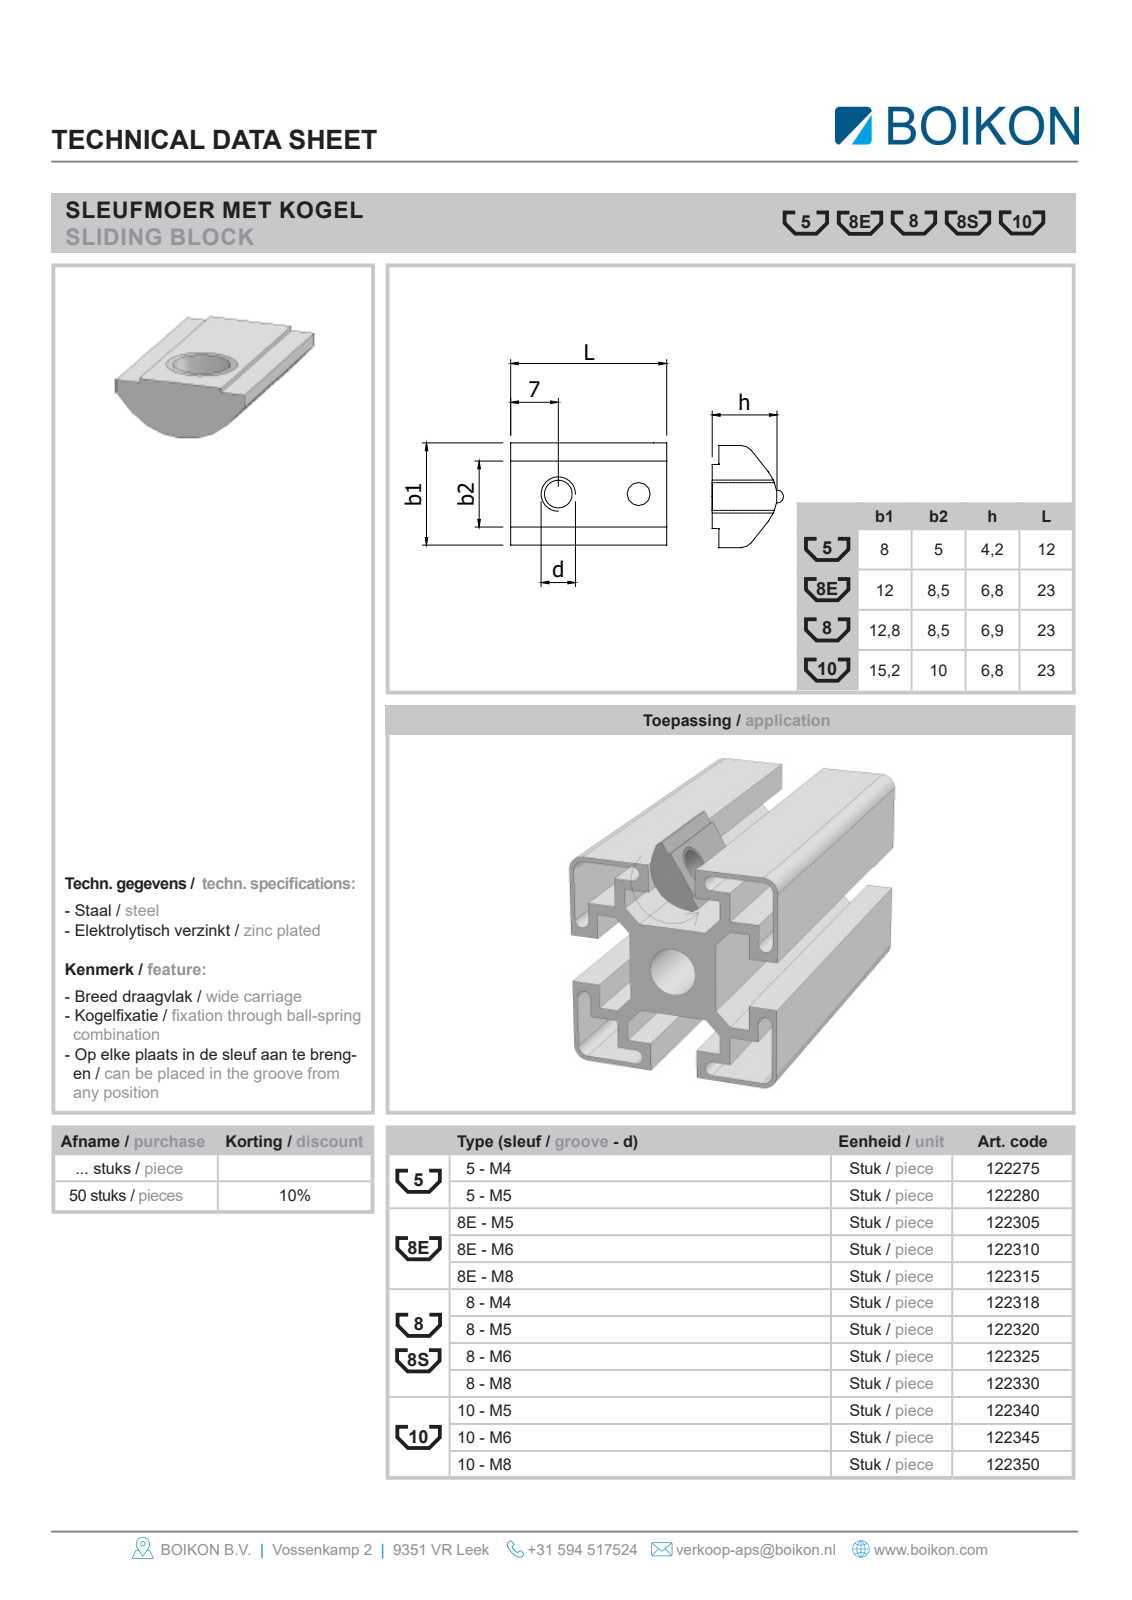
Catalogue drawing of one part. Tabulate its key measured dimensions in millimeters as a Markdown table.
| quantity | value |
| --- | --- |
| part name | Root; 122345Sleufmoer 10 - M6 met kogelBOIKON |
| STEP written by | HiCAD 2013 1802.4 Build 509 (AUTOMOTIVE_DESIGN) |
| units | millimeters |
| bodies | 1 solid, 14 faces (11 planar, 2 cylindrical, 1 other) |
| overall size | 23 × 15.3 × 13.1 |
| volume | 1 597 mm³ |
| surface area | 1 095 mm² |
| round holes (diameter × count) | 6 × 1 |
| partial cylindrical surfaces (radius × count) | 8 × 1 |
| main face-to-face distances | 0.5, 23, 15.3, 2.75, 12.55, 9.8 |
